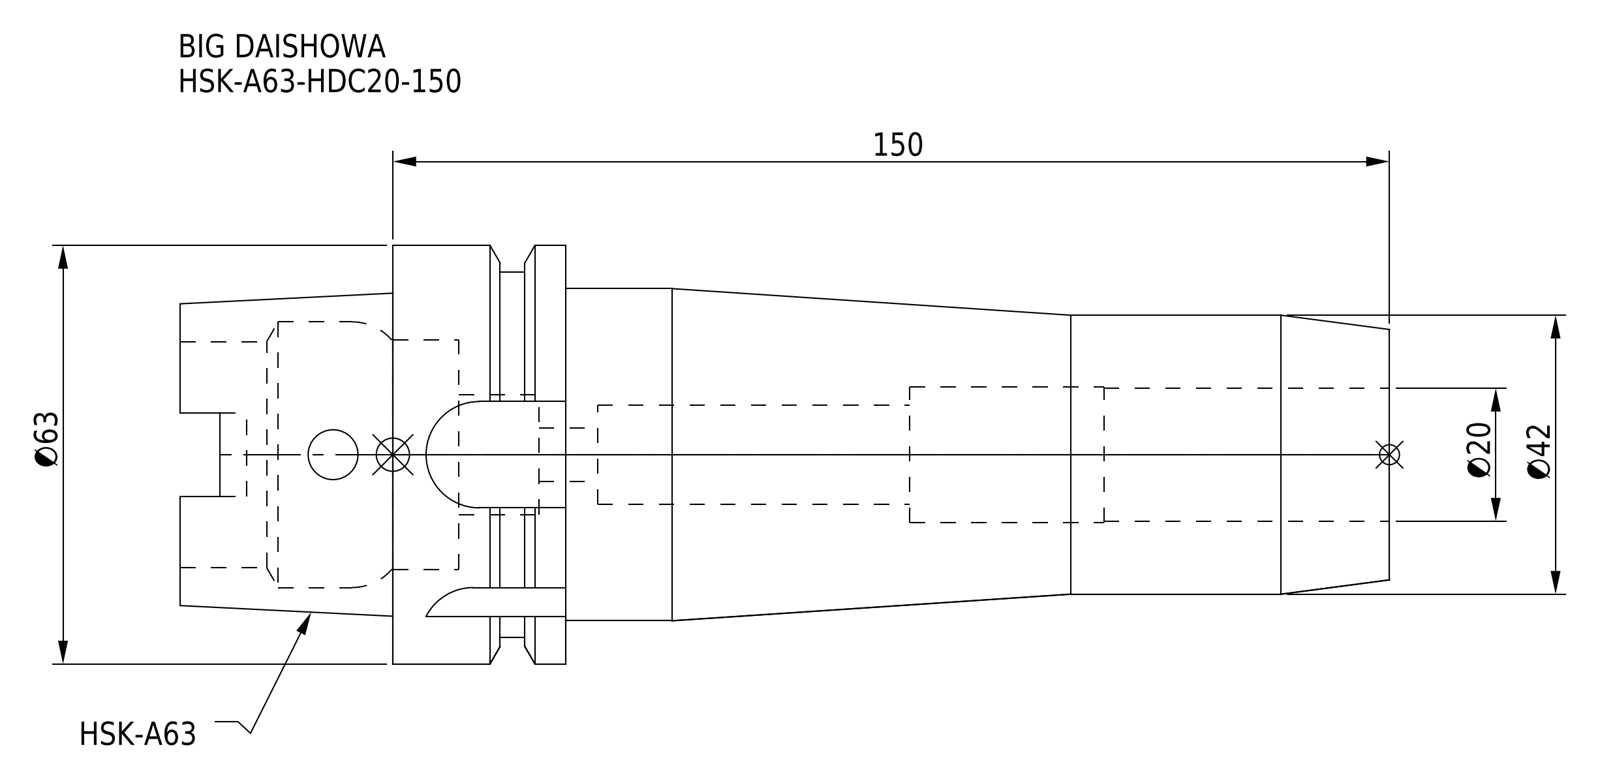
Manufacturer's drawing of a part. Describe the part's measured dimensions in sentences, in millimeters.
The part is named "HSK-A63-HDC20-150". Its 3-D file was written by "CREO PARAMETRIC BY PTC INC, 2016380 (AUTOMOTIVE_DESIGN)". It is 1 solid with 98 faces: 39 planar, 41 cylindrical and 18 other. Overall it measures 182 by 63 by 63 millimeters. Its volume is 245 566 cubic millimeters and its surface area 45 863 square millimeters. Round holes: 1 of diameter 7.5, 1 of diameter 8, 1 of diameter 15, 1 of diameter 18, 1 of diameter 20, 1 of diameter 20.5, 1 of diameter 34, 1 of diameter 34.5, 1 of diameter 40. Round bosses or shafts: 1 of diameter 63, 1 of diameter 55, 1 of diameter 50, 1 of diameter 42. Partial cylindrical surfaces (rounded edges, fillets, slot ends): 4 of radius 2.88, 4 of radius 8. The main face-to-face distances are 26, 124, 150, 140.05, 16.05, 9.95, 182, 58, 41.95, 32.
